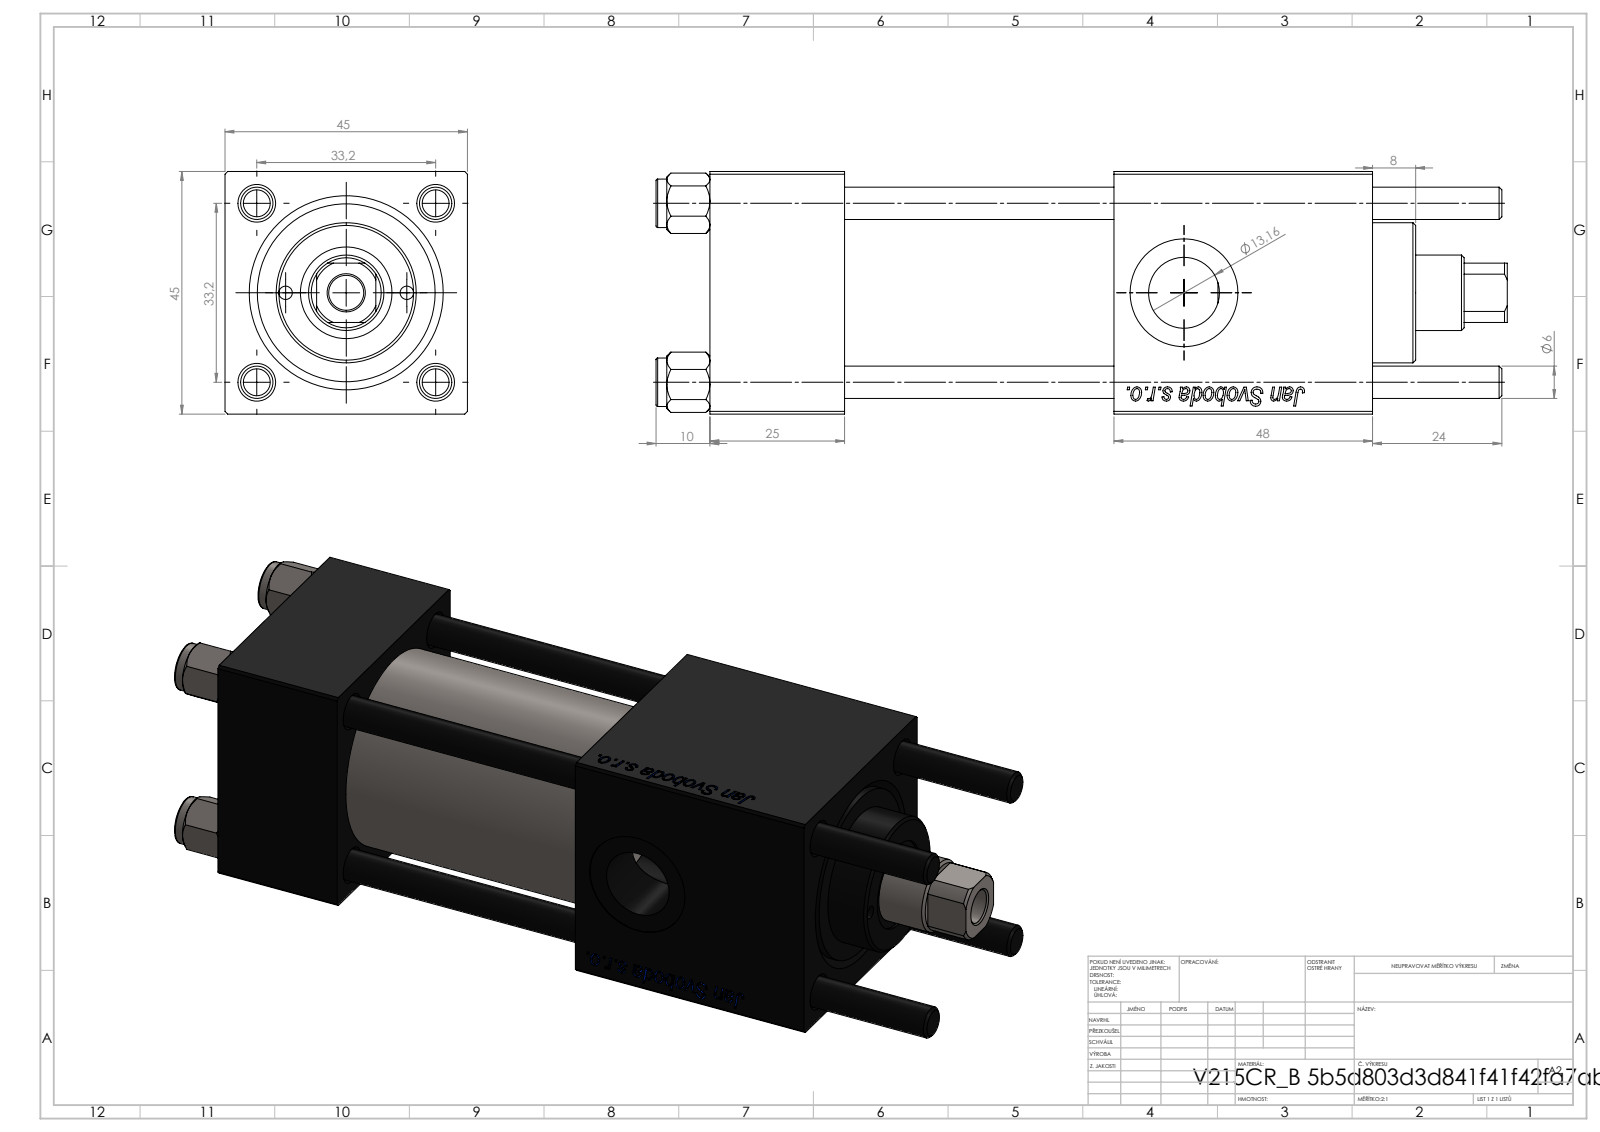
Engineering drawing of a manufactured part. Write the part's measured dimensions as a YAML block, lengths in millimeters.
part_name: "V215_VC_A; V215CR_B_TYCINKA; NUT_M5_B; V215CR_VCP_B (+1 more)"
step_written_by: "SolidWorks 2019 (CONFIG_CONTROL_DESIGN)"
units: millimeters
bodies: {solids: 11, faces: 1161, planar: 431, cylindrical: 82, other: 648}
overall_size: [158, 45, 45]
volume: 198491
surface_area: 72702
round_holes:
  - {diameter: 6, count: 4}
  - {diameter: 2.5, count: 2}
  - {diameter: 7, count: 2}
  - {diameter: 13.16, count: 2}
  - {diameter: 20, count: 2}
  - {diameter: 6.5, count: 1}
  - {diameter: 14, count: 1}
  - {diameter: 17, count: 1}
  - {diameter: 24, count: 1}
  - {diameter: 32, count: 1}
  - {diameter: 33, count: 1}
round_bosses_or_shafts:
  - {diameter: 9, count: 4}
  - {diameter: 38, count: 1}
  - {diameter: 26, count: 1}
partial_cylinders:
  - {radius: 6.5, count: 1}
face_to_face_distances: [45, 25, 123, 98, 50, 75, 48, 94.3, 69.3, 19.3]
hole_center_spacings: [17.44, 23.48, 32.42, 33.2, 11.25, 46.95, 22.5, 75.5]
